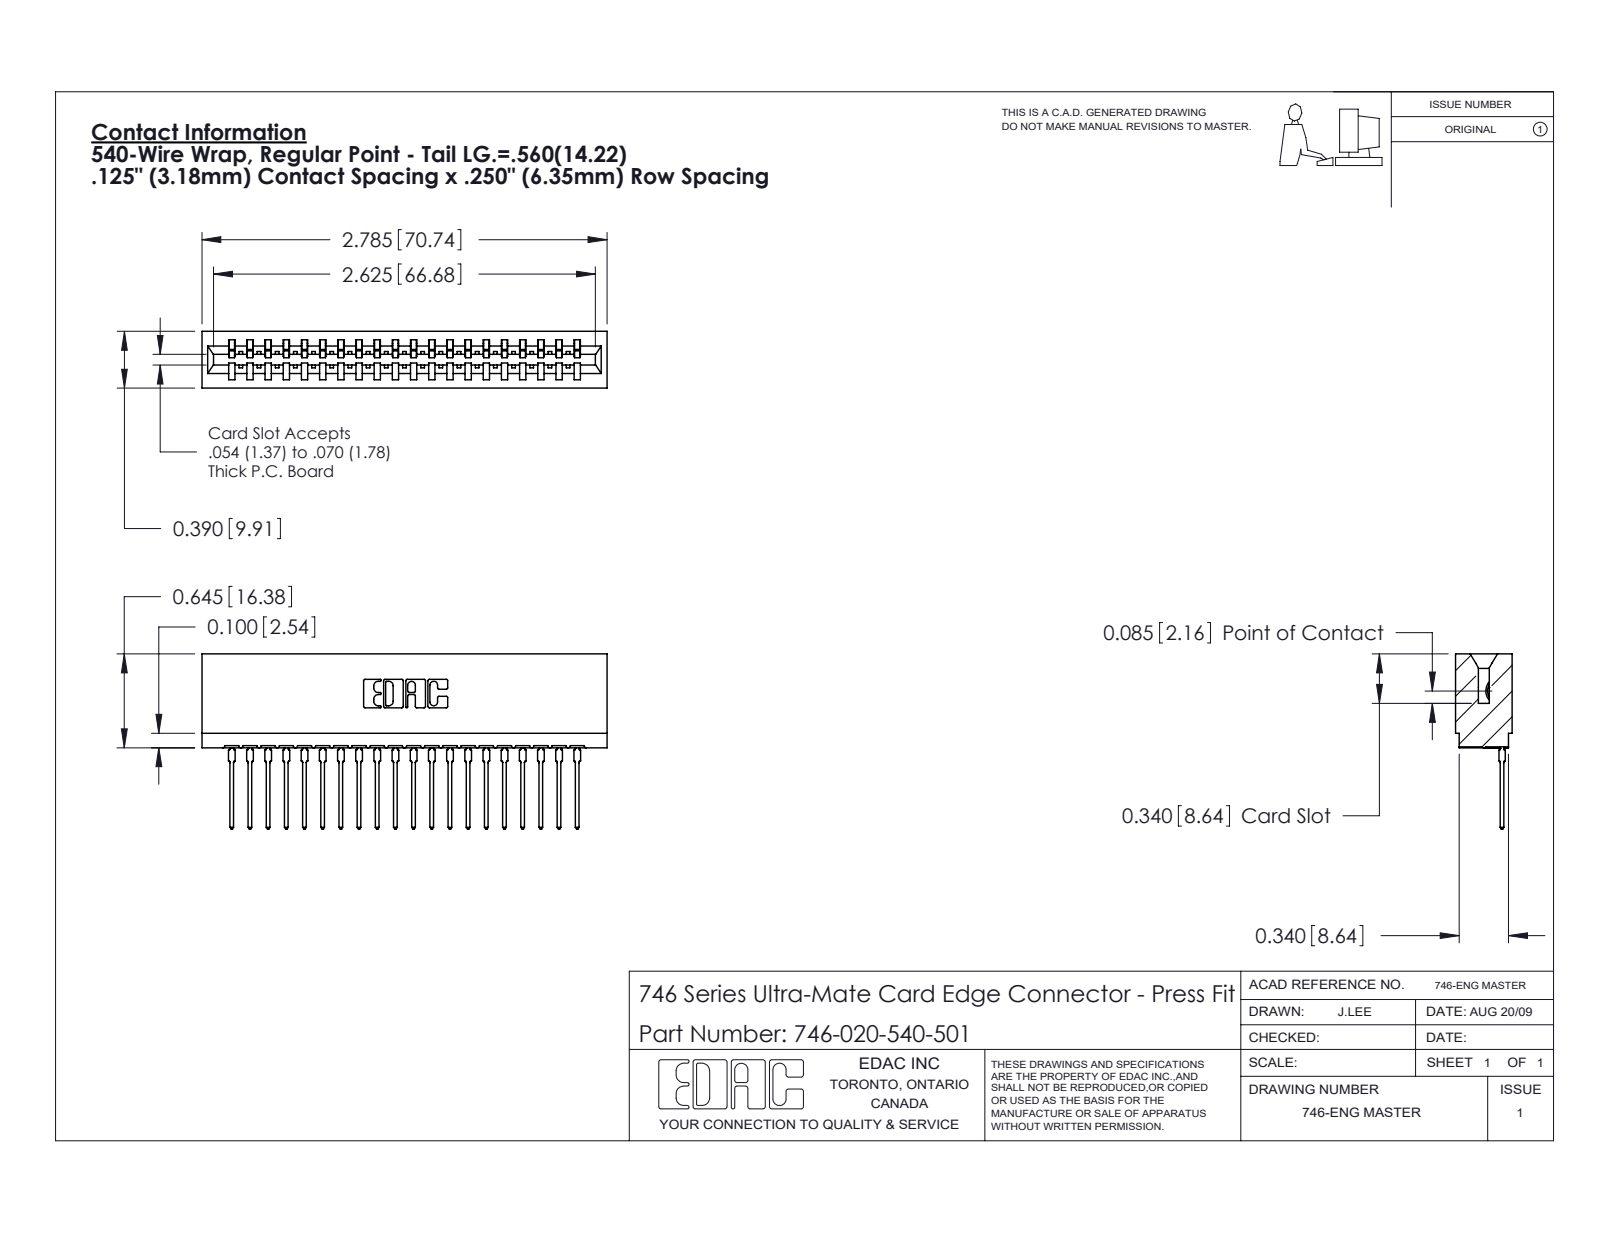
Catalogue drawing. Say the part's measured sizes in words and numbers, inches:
The part is named "746 Part_.340 Slot Depth - 01; 746-292-001_540; 746-020-540-501". Its 3-D file was written by "SolidWorks 2020 (CONFIG_CONTROL_DESIGN)". It is 21 solids with 2257 faces: 1315 planar, 422 cylindrical and 520 other. Overall it measures 2.785 by 1.204 by 0.39 inches. Its volume is 0.496 cubic inches and its surface area 16.84 square inches. Partial cylindrical surfaces (rounded edges, fillets, slot ends): 40 of radius 0.021, 22 of radius 0.01, 21 of radius 0.015, 6 of radius 0.007, 6 of radius 0.031, 4 of radius 0.005, 4 of radius 0.011, 3 of radius 0.026. The main face-to-face distances are 0.25, 0.057, 0.333, 0.39, 0.5, 0.025, 0.307, 0.125, 0.292, 0.125.
